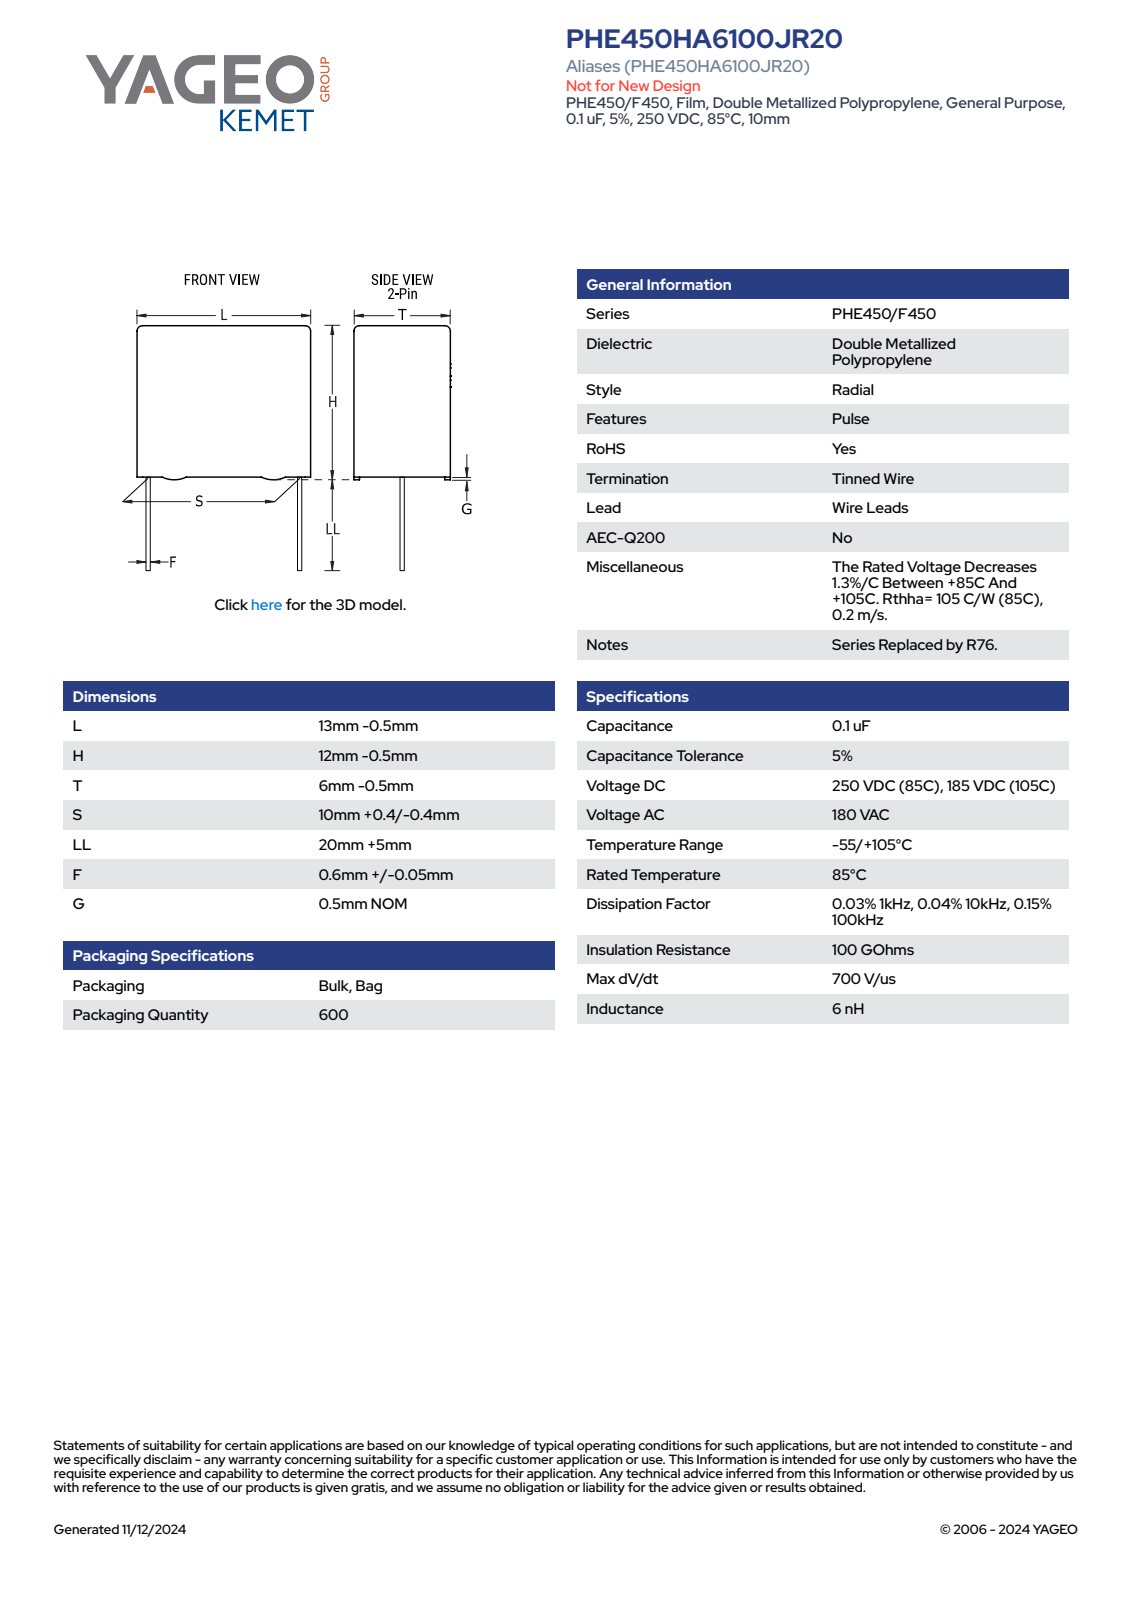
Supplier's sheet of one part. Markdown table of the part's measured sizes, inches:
| quantity | value |
| --- | --- |
| part name | CFR_RBG_13X12X6_L12.5H11.5T5.5S10LL25F0.65G0.5 |
| STEP written by | SolidWorks 2014 (AUTOMOTIVE_DESIGN) |
| units | inches |
| bodies | 4 solids, 89 faces (81 planar, 8 cylindrical, 0 other) |
| overall size | 1.437 × 0.492 × 0.217 |
| volume | 0.047 in³ |
| surface area | 1.02 in² |
| round bosses / shafts (diameter × count) | 0.026 × 2 |
| partial cylindrical surfaces (radius × count) | 0.02 × 4 |
| main face-to-face distances | 0.217, 0.492, 0.433, 0.012, 0.204, 0.02, 0.453, 0.192, 0.984, 1.004 |
